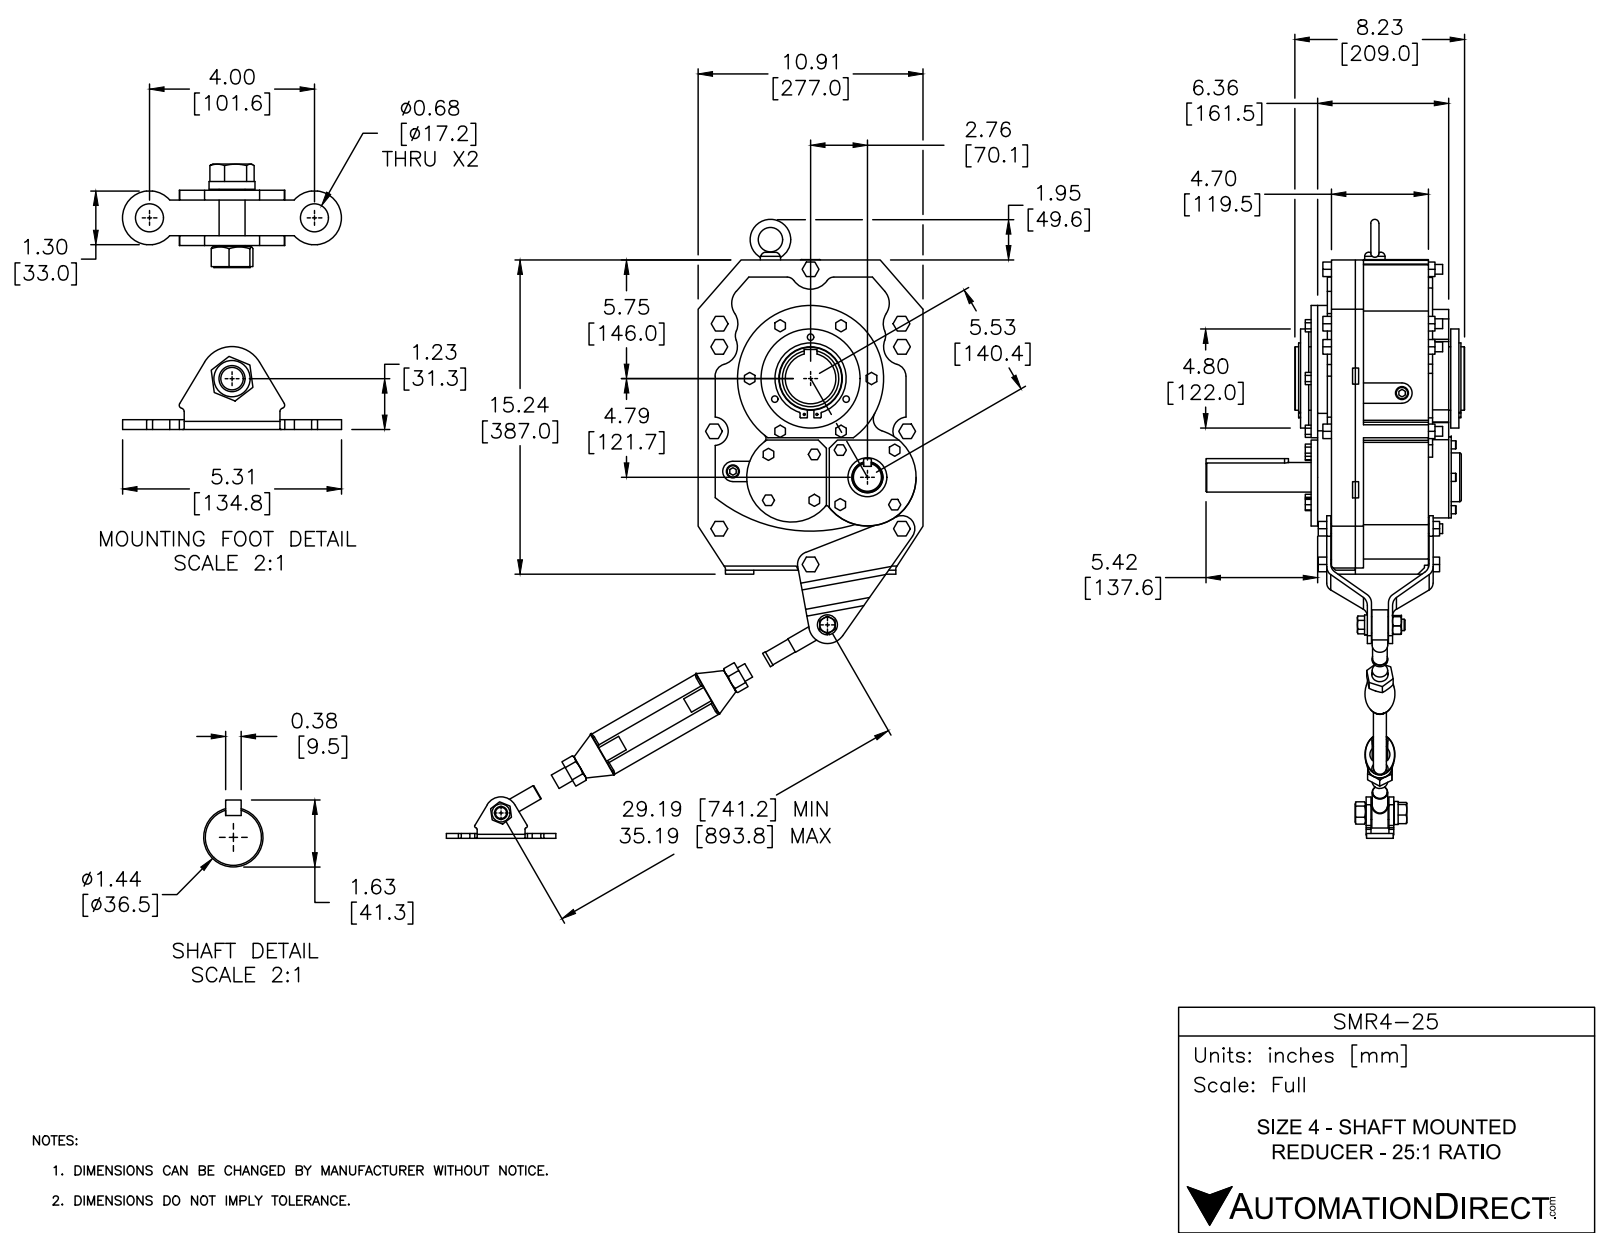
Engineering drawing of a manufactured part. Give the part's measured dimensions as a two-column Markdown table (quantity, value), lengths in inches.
| quantity | value |
| --- | --- |
| part name | SMR4-25; SMR4-TA; SMR4-TA_5; SMR4-TA_4 (+4 more) |
| STEP written by | SolidWorks 2016 (AUTOMOTIVE_DESIGN) |
| units | inches |
| bodies | 74 solids, 1270 faces (715 planar, 430 cylindrical, 125 other) |
| overall size | 31.871 × 26.342 × 12.541 |
| volume | 853 in³ |
| surface area | 1 914 in² |
| round holes (diameter × count) | 0.512 × 10, 0.63 × 6, 0.422 × 4, 0.531 × 4, 0.313 × 3, 0.098 × 2, 0.677 × 2, 0.689 × 2, 0.787 × 2, 0.551 × 1, 0.559 × 1, 0.571 × 1 |
| round bosses / shafts (diameter × count) | 0.472 × 10, 0.75 × 4, 0.394 × 4, 1.457 × 2, 0.711 × 2, 0.63 × 2, 7.087 × 1, 4.803 × 1 |
| partial cylindrical surfaces (radius × count) | 0.118 × 17, 0.394 × 11, 0.492 × 6, 0.591 × 6, 0.689 × 6, 0.886 × 6, 0.039 × 4, 0.079 × 4 |
| main face-to-face distances | 0.197, 1.831, 0.984, 5.689, 0.236, 0.787, 6.358, 5.886, 4.902, 0.315 |
| hole center spacings | 3.11, 4.398, 2, 8.819, 10.266, 1.122, 1.287, 1.609 |
